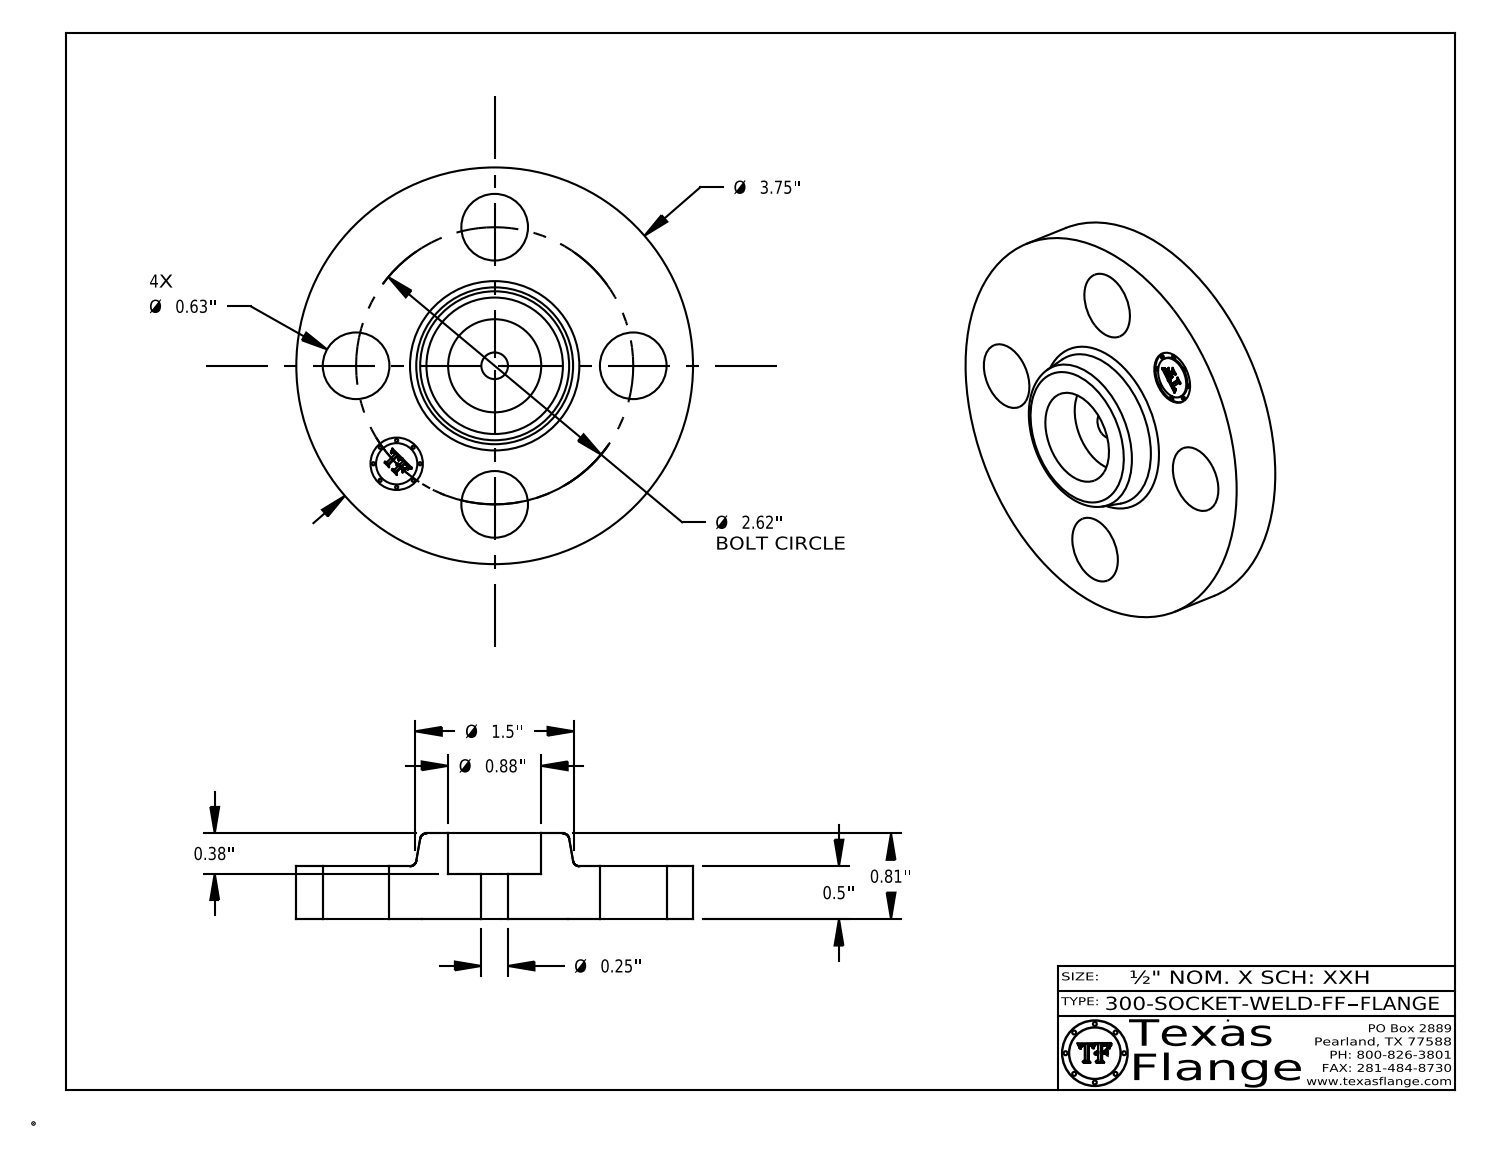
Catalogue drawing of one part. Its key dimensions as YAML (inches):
part_name: "300-SOCKET-WELD-FF"
step_written_by: "CATIA V5 STEP AP214 (AUTOMOTIVE_DESIGN)"
units: inches
bodies: {solids: 1, faces: 410, planar: 370, cylindrical: 34, other: 6}
overall_size: [3.75, 3.75, 0.81]
volume: 5.154
surface_area: 31.86
round_holes:
  - {diameter: 0.63, count: 4}
  - {diameter: 0.252, count: 1}
  - {diameter: 0.495, count: 1}
  - {diameter: 0.88, count: 1}
round_bosses_or_shafts:
  - {diameter: 0.03, count: 8}
  - {diameter: 3.75, count: 1}
  - {diameter: 0.39, count: 1}
face_to_face_distances: [0.5, 0.81, 0.31, 0.07, 0.43, 0.38, 0.485, 0.055, 0.015, 0.325]
hole_center_spacings: [1.31, 1.852, 1.003, 2.42, 2.62, 1.31]
